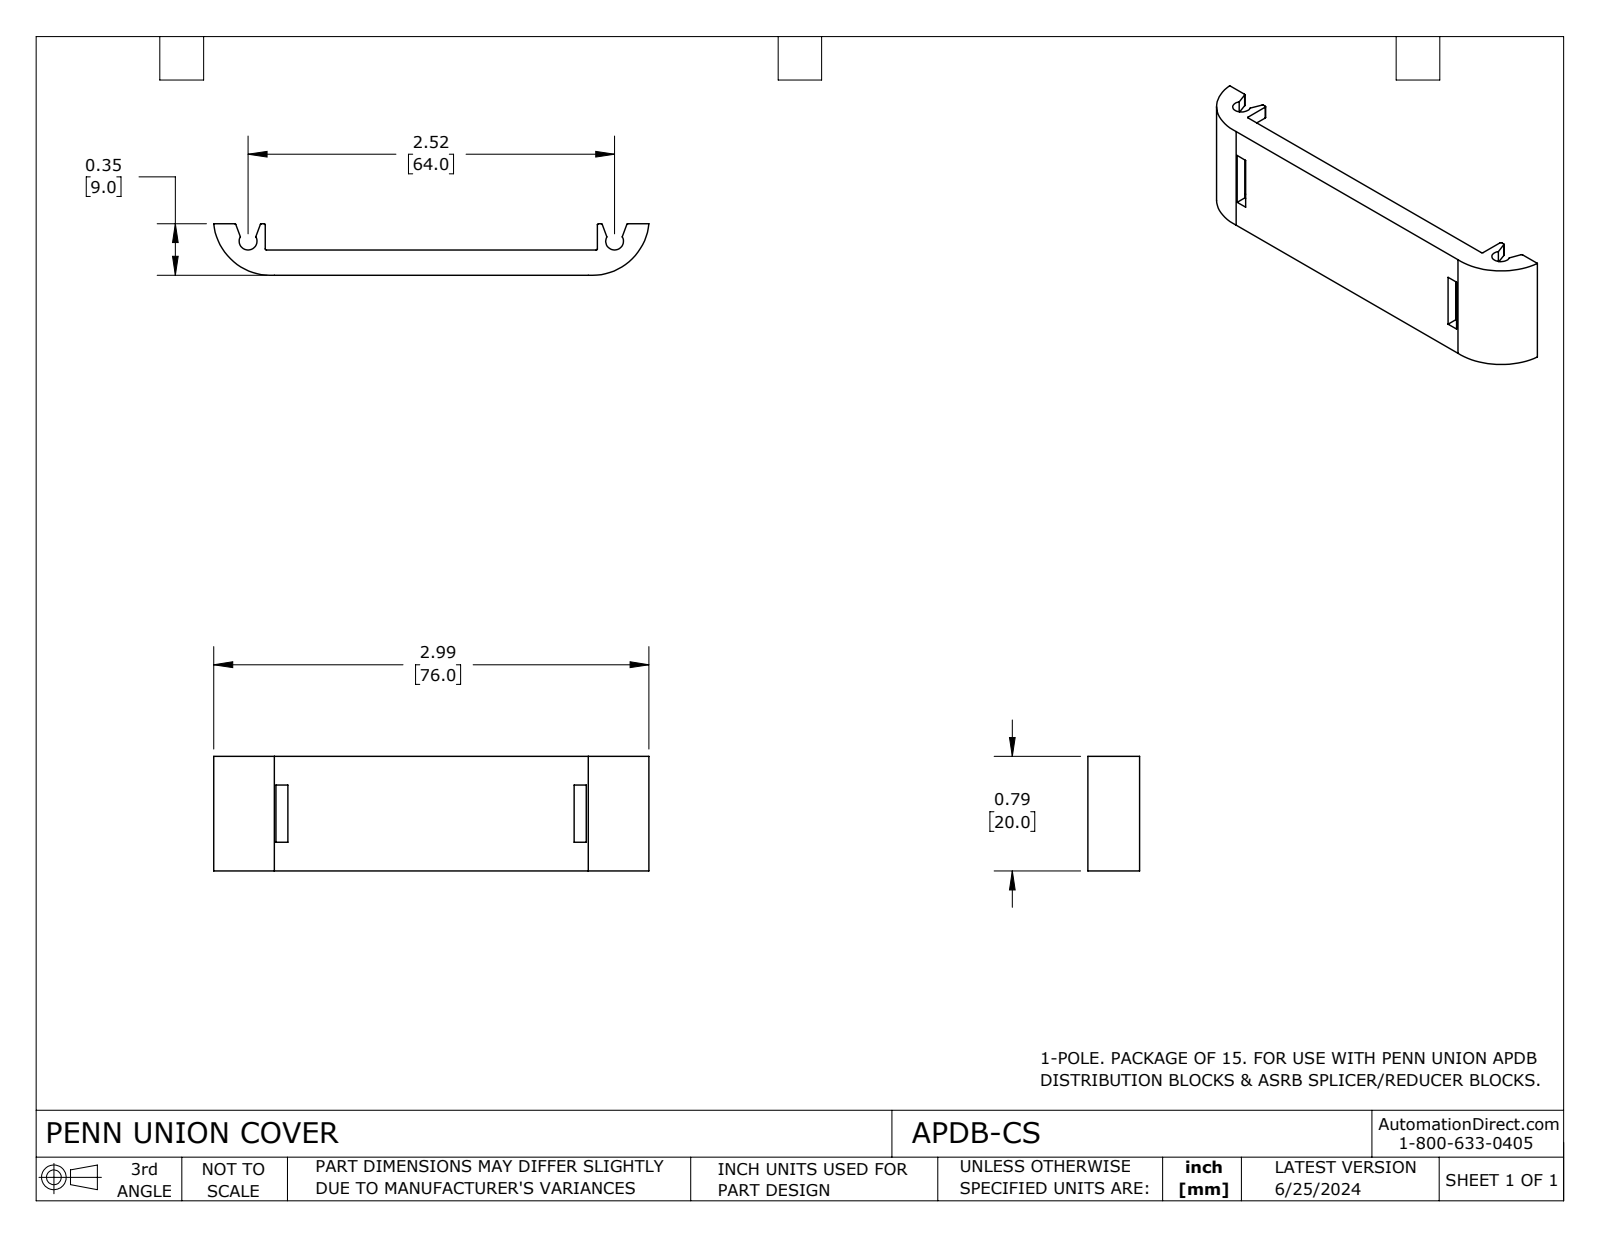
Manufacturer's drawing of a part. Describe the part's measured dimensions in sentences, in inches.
The part is named "APDB-CS". Its 3-D file was written by "SolidWorks 2023 (CONFIG_CONTROL_DESIGN)". It is 1 solid with 66 faces: 34 planar, 32 cylindrical and 0 other. Overall it measures 2.992 by 0.787 by 0.355 inches. Its volume is 0.244 cubic inches and its surface area 7.002 square inches. Partial cylindrical surfaces (rounded edges, fillets, slot ends): 8 of radius 0.008, 2 of radius 0.061, 2 of radius 0.348, 2 of radius 0.394. The main face-to-face distances are 0.075, 0.091, 0.697, 0.787, 0.098, 0.173, 0.606, 0.181, 0.28, 0.354.
